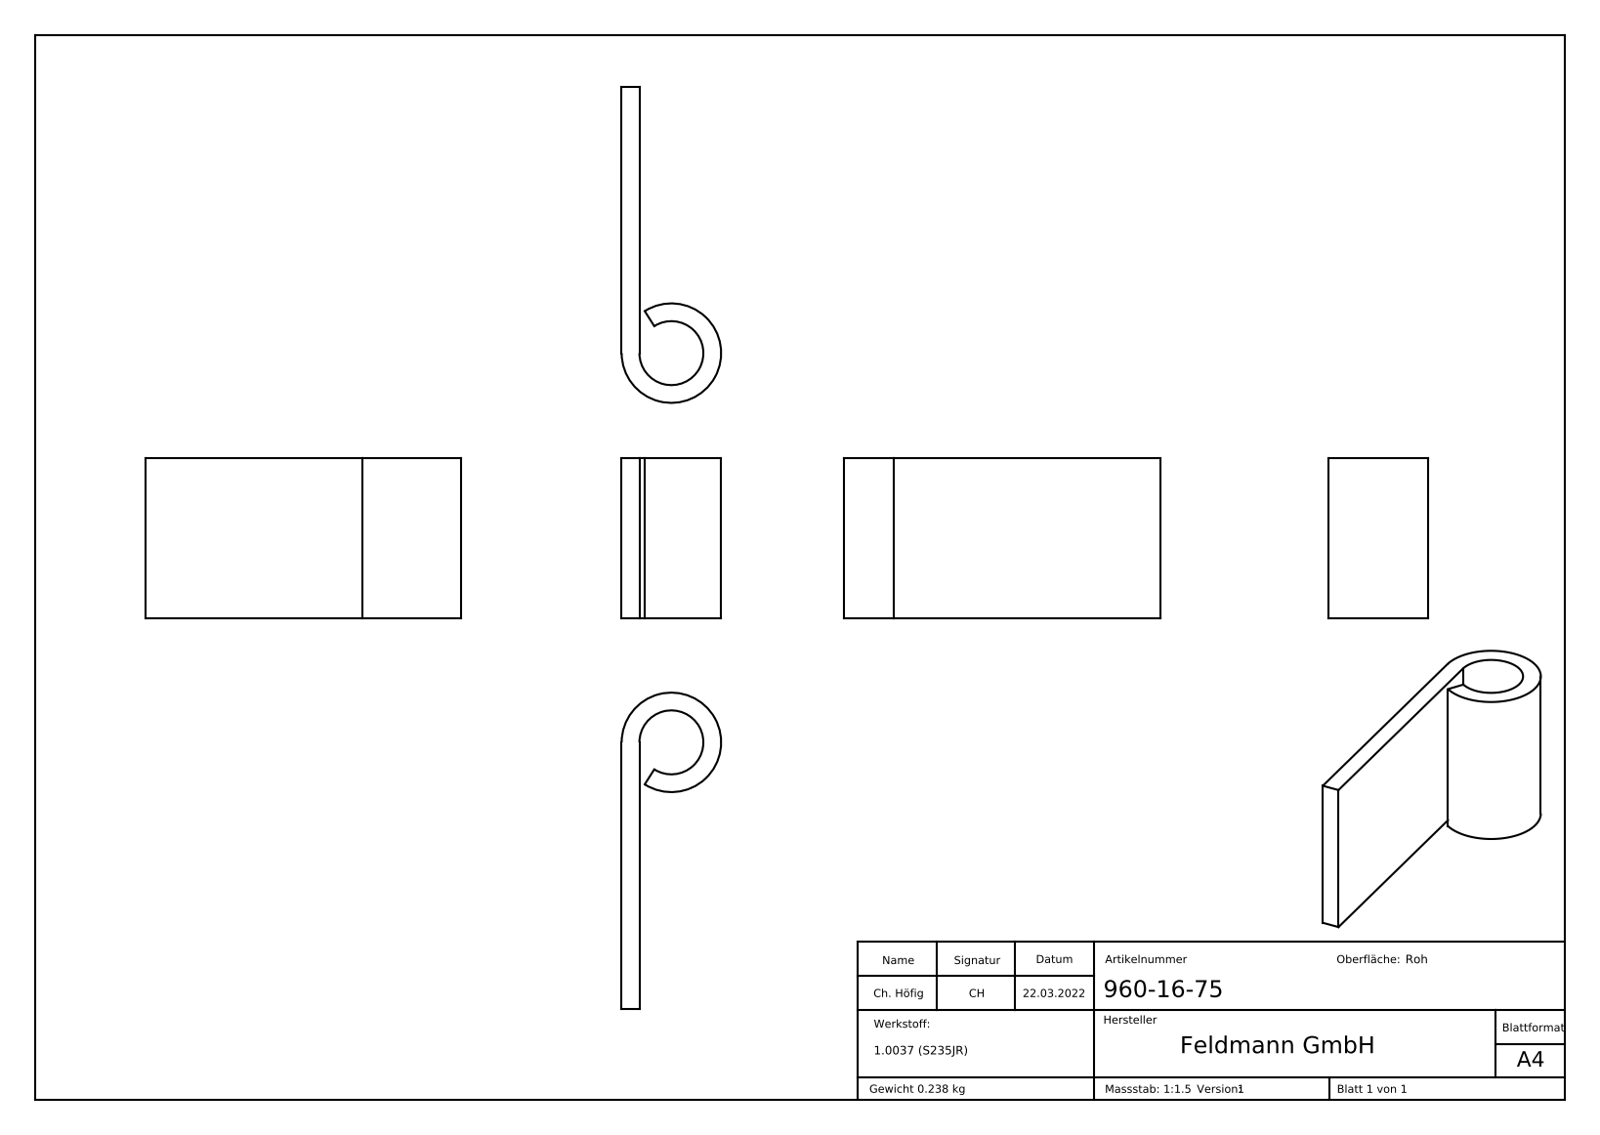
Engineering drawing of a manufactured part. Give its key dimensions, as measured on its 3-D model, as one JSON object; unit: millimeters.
{"part_name": "960-16-75", "step_written_by": "SolidWorks 2018 (CONFIG_CONTROL_DESIGN)", "units": "millimeters", "bodies": {"solids": 1, "faces": 213, "planar": 119, "cylindrical": 2, "other": 92}, "overall_size": [89, 45, 28], "volume_mm3": 30531, "surface_area_mm2": 14028, "round_holes": [[18, 1]], "round_bosses_or_shafts": [[28, 1]], "face_to_face_distances": [5, 45, 2.97, 1.25, 1.64, 0.39, 5.73, 2.02, 1.37, 3.27]}
